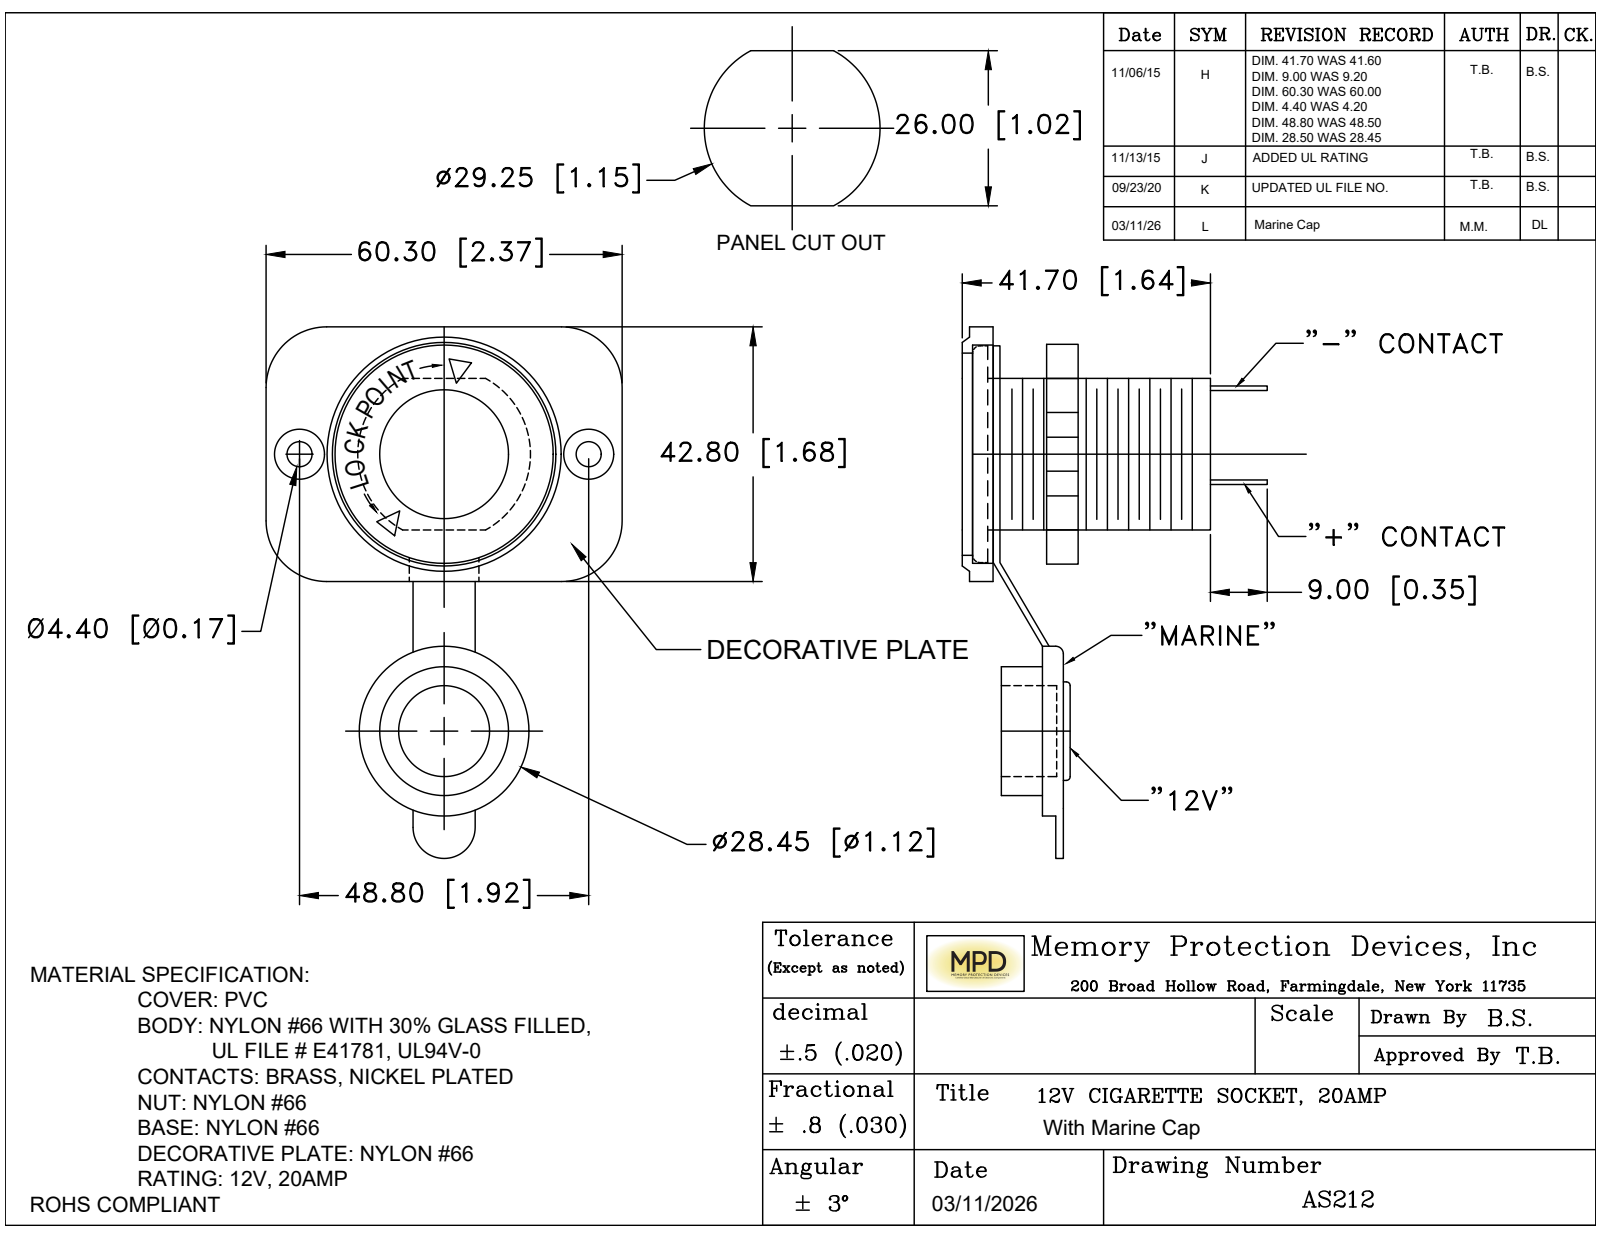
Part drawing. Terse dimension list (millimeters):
name: AS212
written by: SolidWorks 2017 (AUTOMOTIVE_DESIGN)
unit: mm
bodies: 5 solids, 303 faces (69 planar, 115 cylindrical, 119 other)
size: 89.45 × 60.3 × 50.7
volume: 29 950 mm³; area: 18 284 mm²
holes: 2× ⌀4.4, 1× ⌀2, 1× ⌀15.5, 1× ⌀21.5, 1× ⌀24.5, 1× ⌀33.8
bosses: 1× ⌀36, 1× ⌀29, 1× ⌀28.45, 1× ⌀26.83, 1× ⌀21.5, 1× ⌀19
rounds: 4× R10, 3× R2, 1× R1, 1× R5.25, 1× R16.5, 1× R18.5
face distances: 4, 1, 1.5, 11.8, 36.55, 14.3, 40.55, 2.5, 9, 13
hole spacings: 24.4, 52.6, 46.6, 48.8
